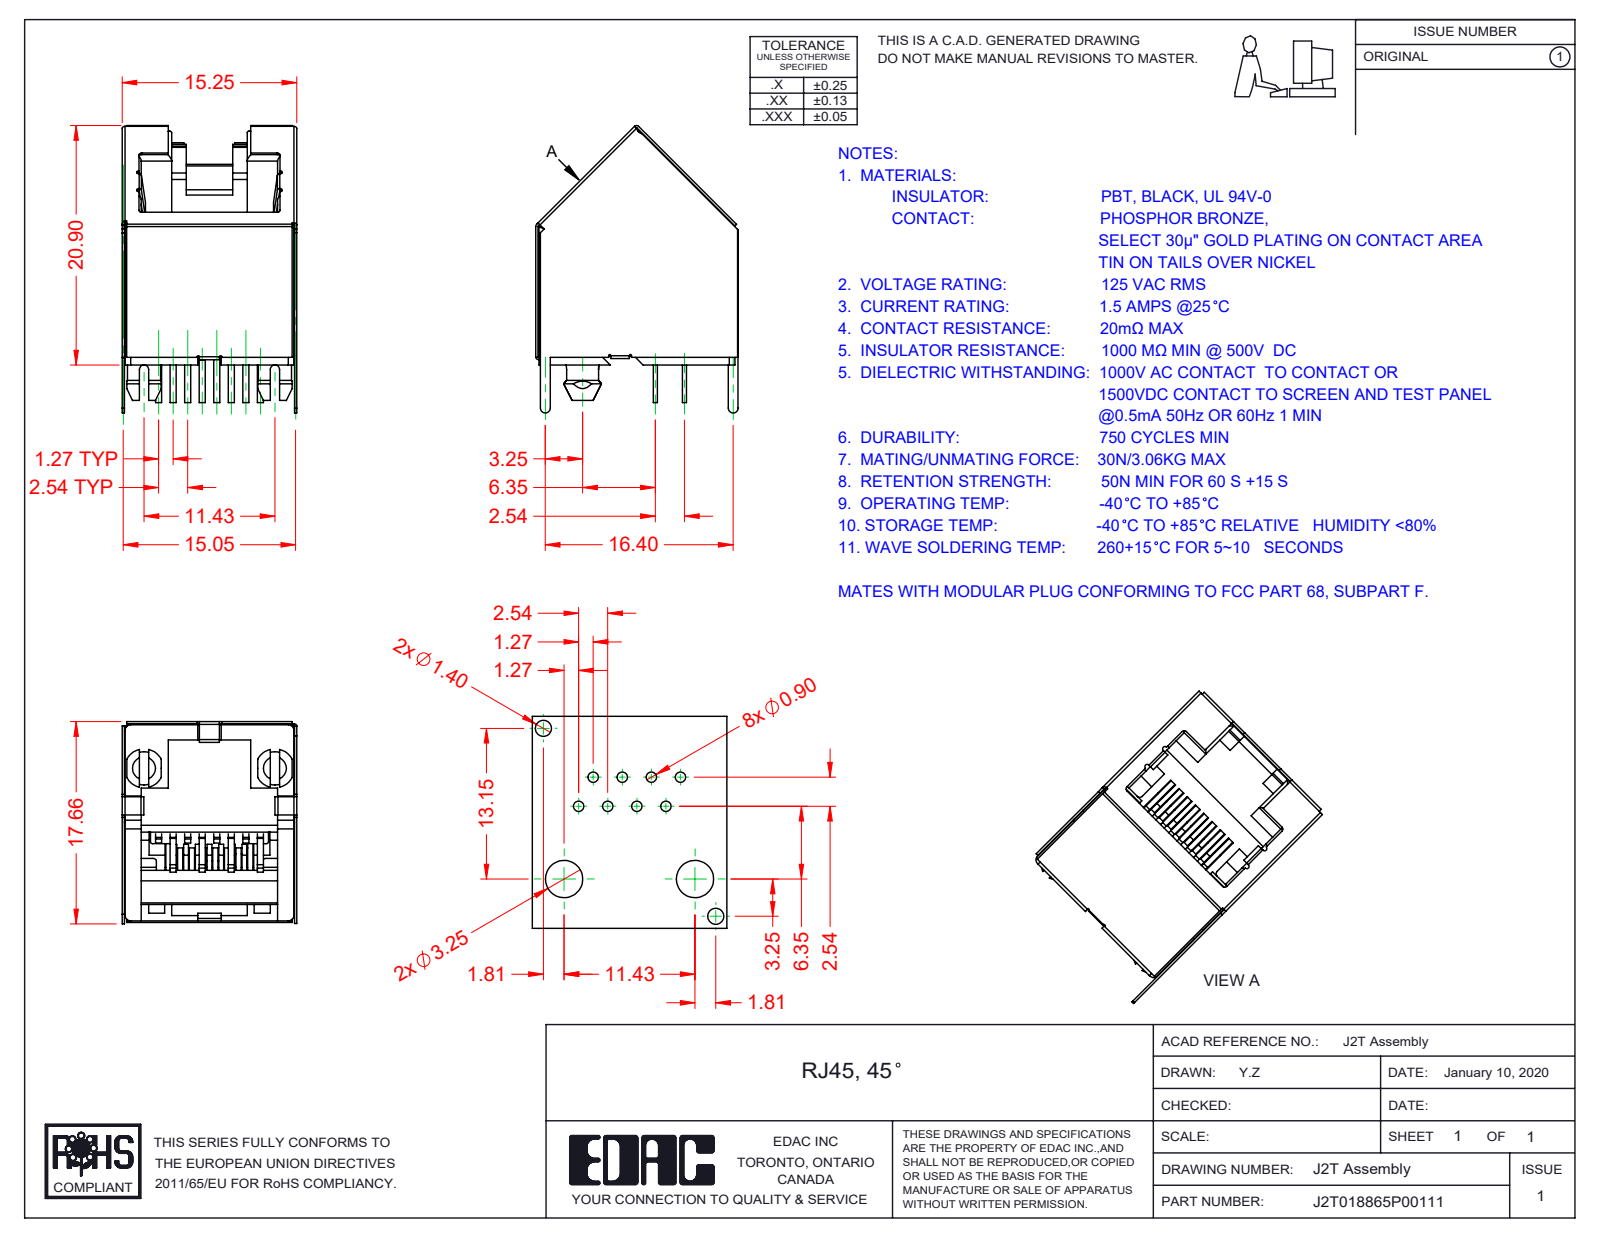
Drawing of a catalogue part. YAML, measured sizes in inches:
part_name: "2T Contacts; 2T Insulator; 2T Shell; RJ2T018865P00111 (+1 more)"
step_written_by: "SolidWorks 2016 (CONFIG_CONTROL_DESIGN)"
units: inches
bodies: {solids: 11, faces: 631, planar: 447, cylindrical: 161, other: 23}
overall_size: [0.988, 0.695, 0.6]
volume: 0.12
surface_area: 8.026
round_bosses_or_shafts:
  - {diameter: 0.114, count: 2}
partial_cylinders:
  - {radius: 0.02, count: 21}
  - {radius: 0.039, count: 16}
  - {radius: 0.008, count: 12}
  - {radius: 0.01, count: 10}
  - {radius: 0.057, count: 8}
  - {radius: 0.06, count: 8}
  - {radius: 0.004, count: 5}
  - {radius: 0.012, count: 3}
face_to_face_distances: [0.592, 0.056, 0.525, 0.583, 0.591, 0.6, 0.584, 0.59, 0.582, 0.581]
